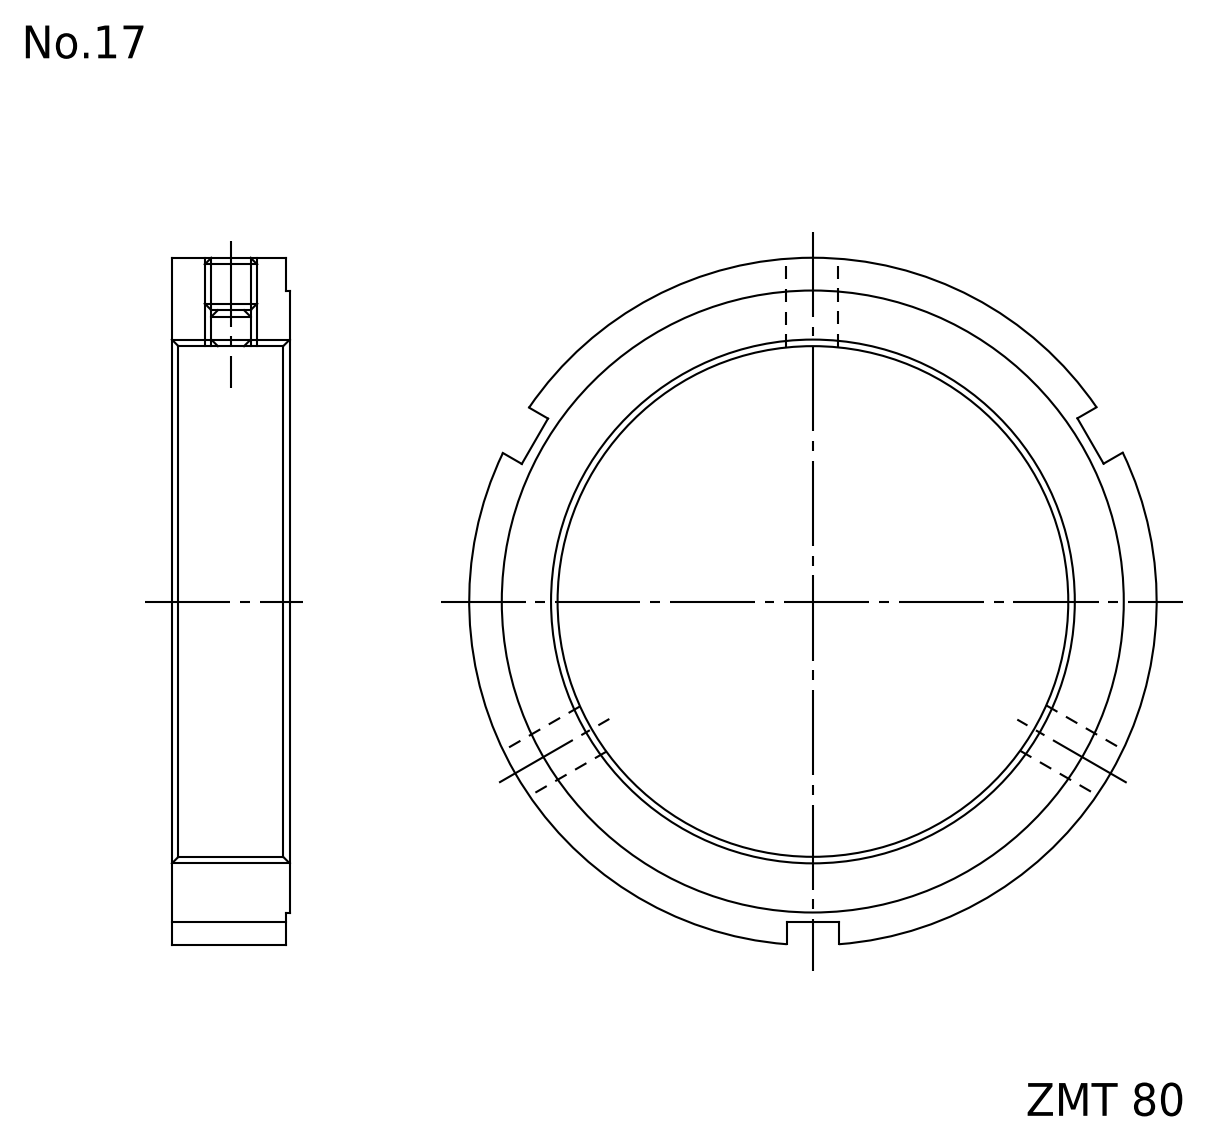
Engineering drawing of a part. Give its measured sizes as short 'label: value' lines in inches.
name: FKD ZMT 80
written by: Autodesk Inventor 2011 (AUTOMOTIVE_DESIGN)
unit: in
bodies: 1 solid, 20 faces (12 planar, 8 cylindrical, 0 other)
size: 4.134 × 4.128 × 0.709
volume: 3.774 in³; area: 28.63 in²
holes: 3× ⌀0.262, 1× ⌀3.15
bosses: 1× ⌀4.134, 1× ⌀3.74
face distances: 0.709, 0.02, 0.689, 0.315
